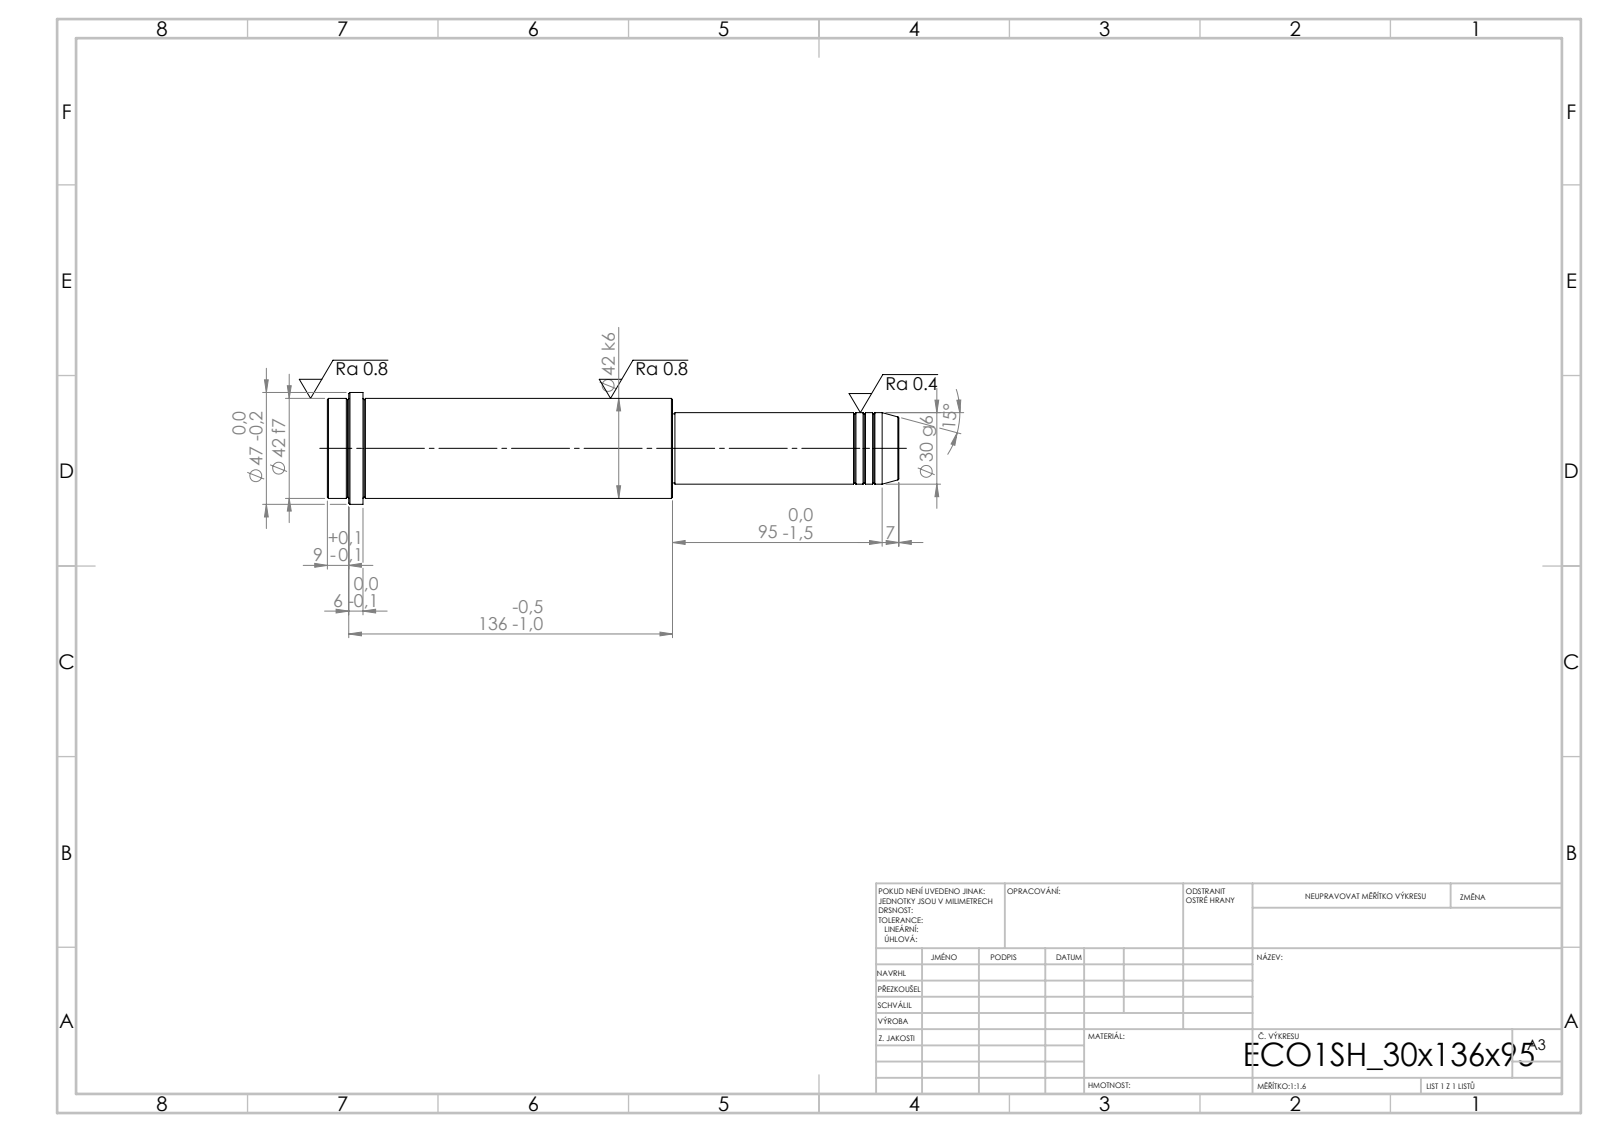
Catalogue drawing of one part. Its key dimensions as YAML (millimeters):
step_written_by: "SolidWorks 2019 (CONFIG_CONTROL_DESIGN)"
units: millimeters
bodies: {solids: 1, faces: 52, planar: 6, cylindrical: 16, other: 30}
overall_size: [240, 47, 47]
volume: 269233
surface_area: 31720
round_bosses_or_shafts:
  - {diameter: 47, count: 1}
  - {diameter: 42, count: 1}
  - {diameter: 30, count: 1}
  - {diameter: 29, count: 1}
face_to_face_distances: [145, 95, 240, 225, 130, 15, 231, 136, 6, 9]
